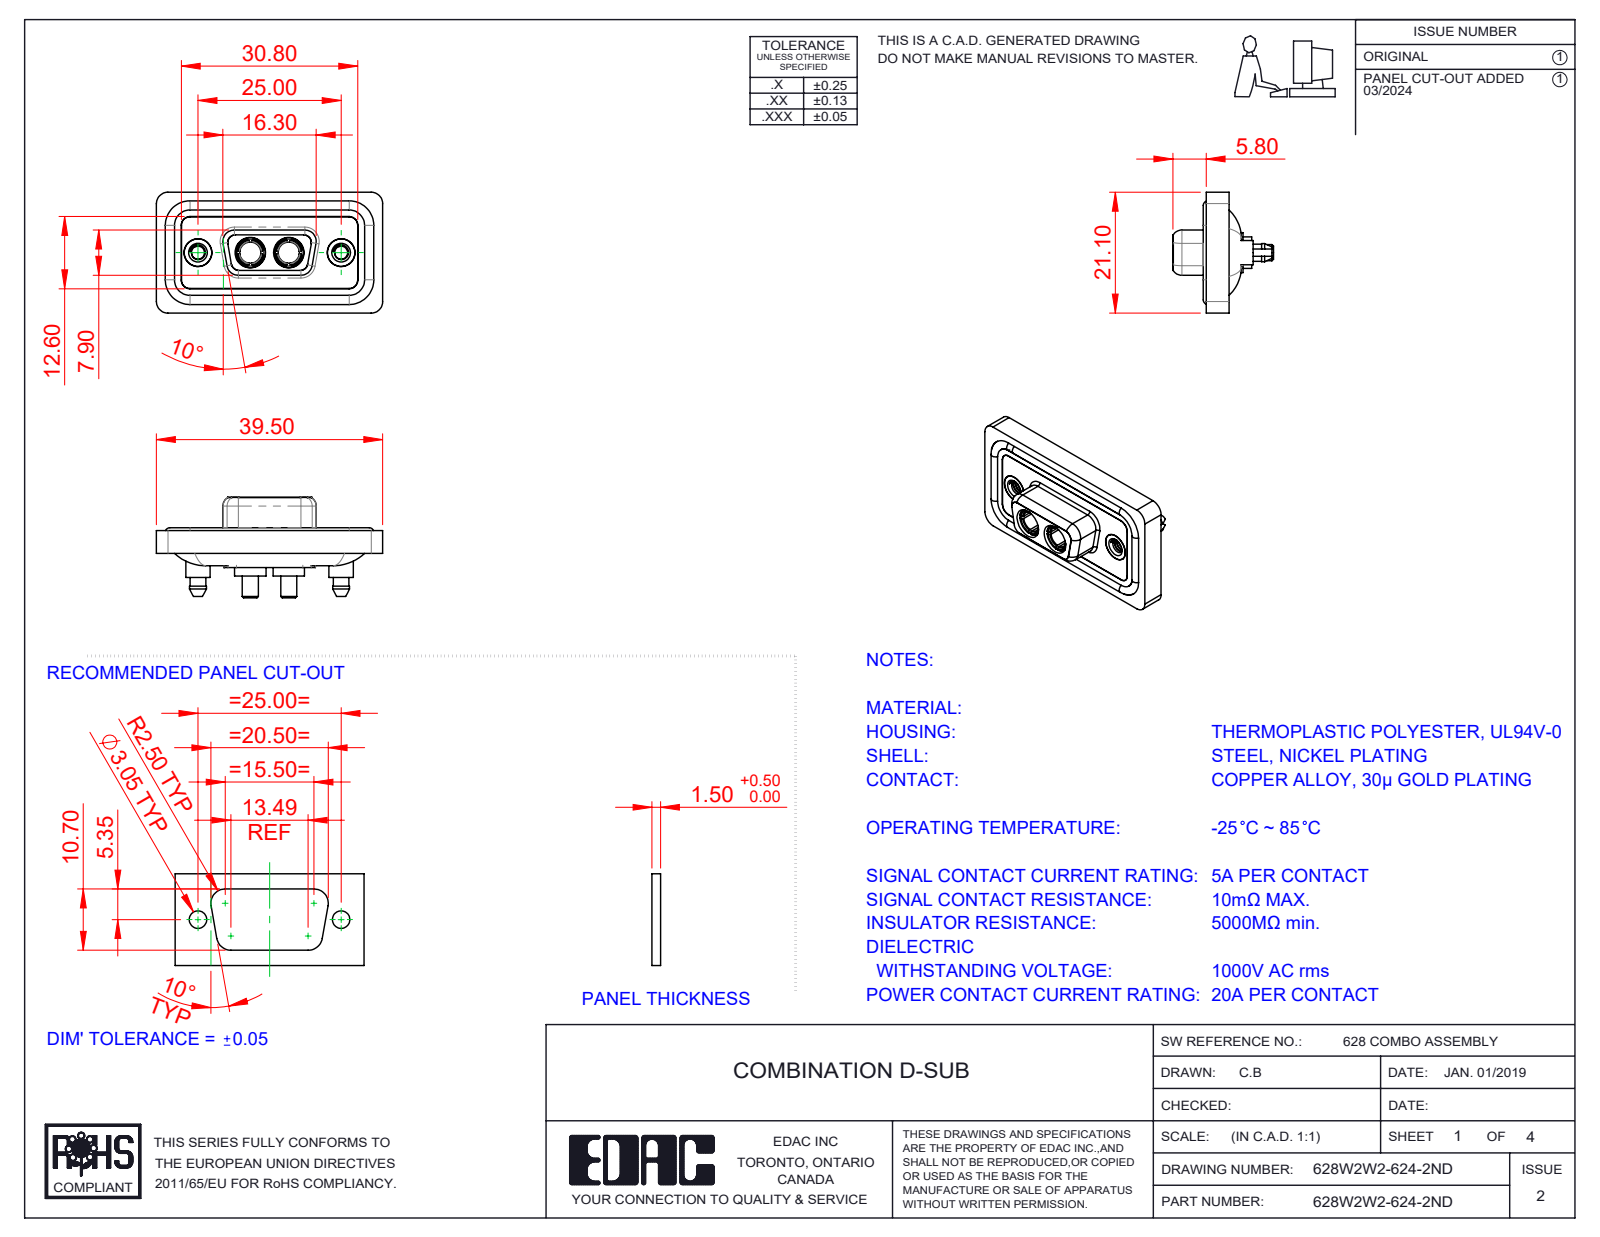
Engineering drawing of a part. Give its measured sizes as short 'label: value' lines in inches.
name: 628Combo Waterproof Housing_09 Contacts; 628W2W2-624-2ND; 628Combo Shell Rear_09 Contacts; 628Combo Shell Front_09 Contacts (+3 more)
written by: SolidWorks 2023 (CONFIG_CONTROL_DESIGN)
unit: in
bodies: 11 solids, 600 faces (179 planar, 282 cylindrical, 139 other)
size: 1.555 × 0.831 × 0.691
volume: 0.296 in³; area: 12.36 in²
holes: 4× ⌀0.191, 2× ⌀0.089, 2× ⌀0.146, 2× ⌀0.157, 2× ⌀0.159, 2× ⌀0.197, 2× ⌀0.209
bosses: 4× ⌀0.063, 2× ⌀0.217, 2× ⌀0.213, 2× ⌀0.205, 2× ⌀0.195, 2× ⌀0.195, 2× ⌀0.189, 2× ⌀0.187
rounds: 24× R0.059, 18× R0.079, 10× R0.063, 8× R0.053, 4× R0.01, 4× R0.02, 4× R0.024, 4× R0.026
face distances: 0.016, 0.071, 0.043, 0.114, 0.063, 0.02, 0.222, 0.293, 0.059, 0.157
hole spacings: 0.36, 0.624, 0.265, 0.984
